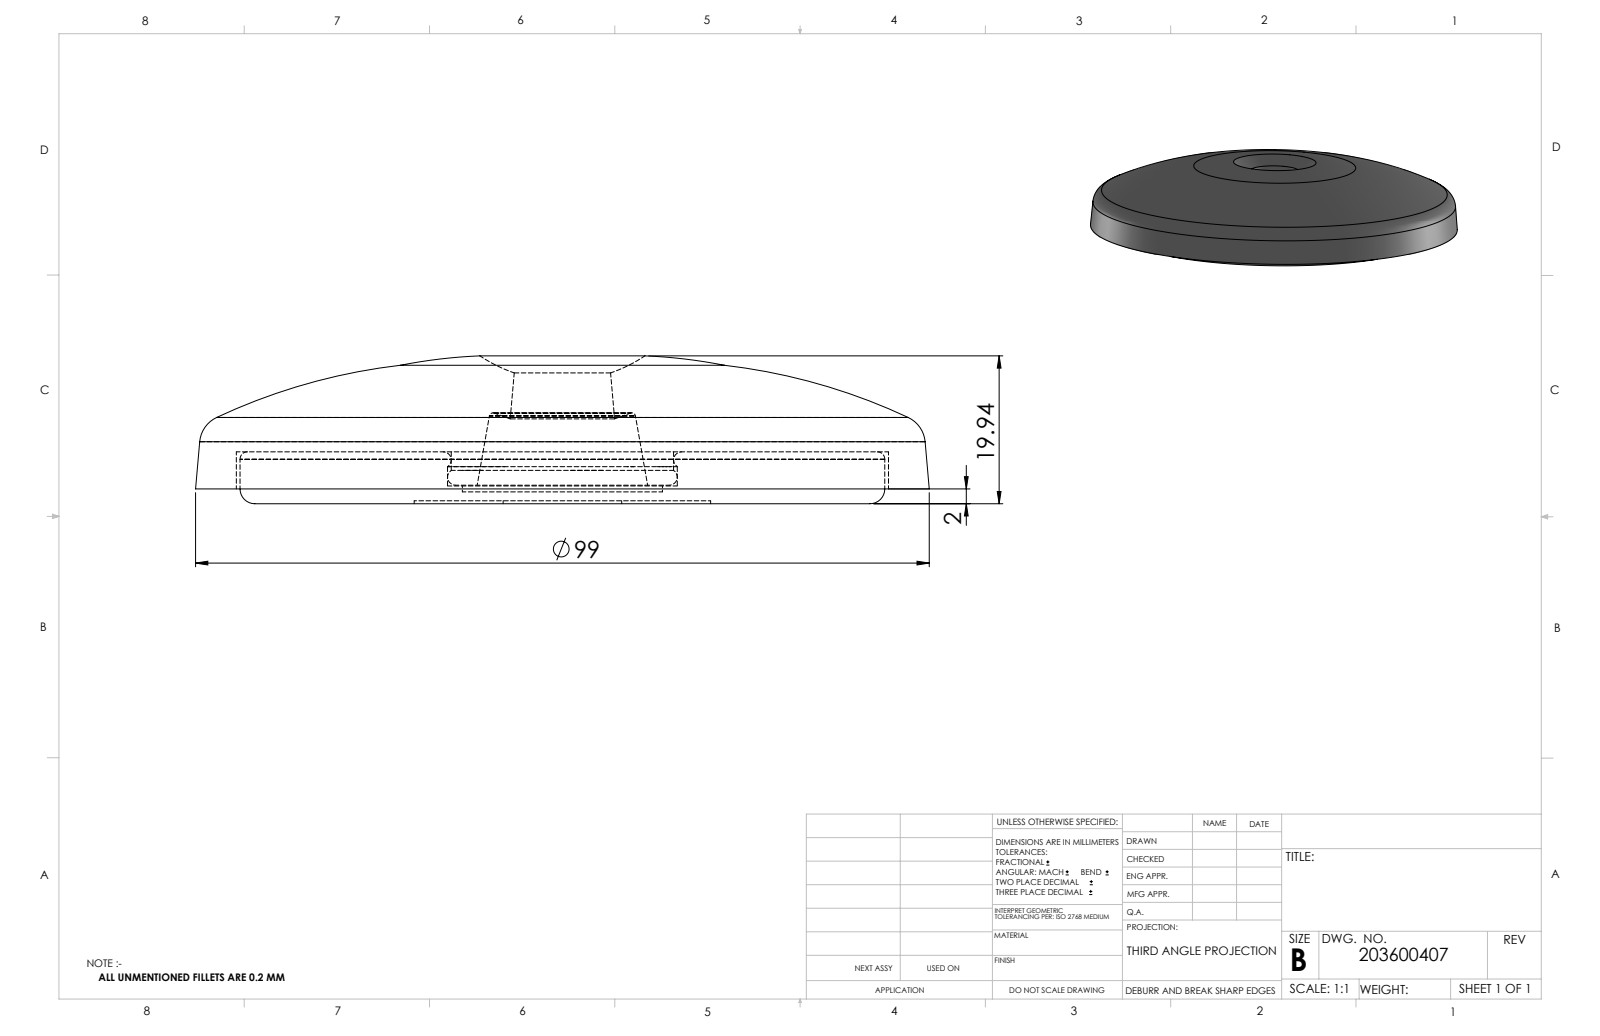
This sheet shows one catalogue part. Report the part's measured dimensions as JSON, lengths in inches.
{"part_name": "203600407_c_1", "step_written_by": "SolidWorks 2014 (CONFIG_CONTROL_DESIGN)", "units": "inches", "bodies": {"solids": 1, "faces": 48, "planar": 9, "cylindrical": 14, "other": 25}, "overall_size": [3.898, 3.898, 0.785], "volume_in3": 6.692, "surface_area_in2": 38.39, "round_holes": [[1.063, 1], [1.22, 1], [1.575, 1], [3.465, 1]], "round_bosses_or_shafts": [[3.425, 1], [1.181, 1], [0.63, 1]], "face_to_face_distances": [0.016, 0.079, 0.063, 0.047, 0.276, 0.26, 0.213, 0.197, 0.098, 0.083]}
